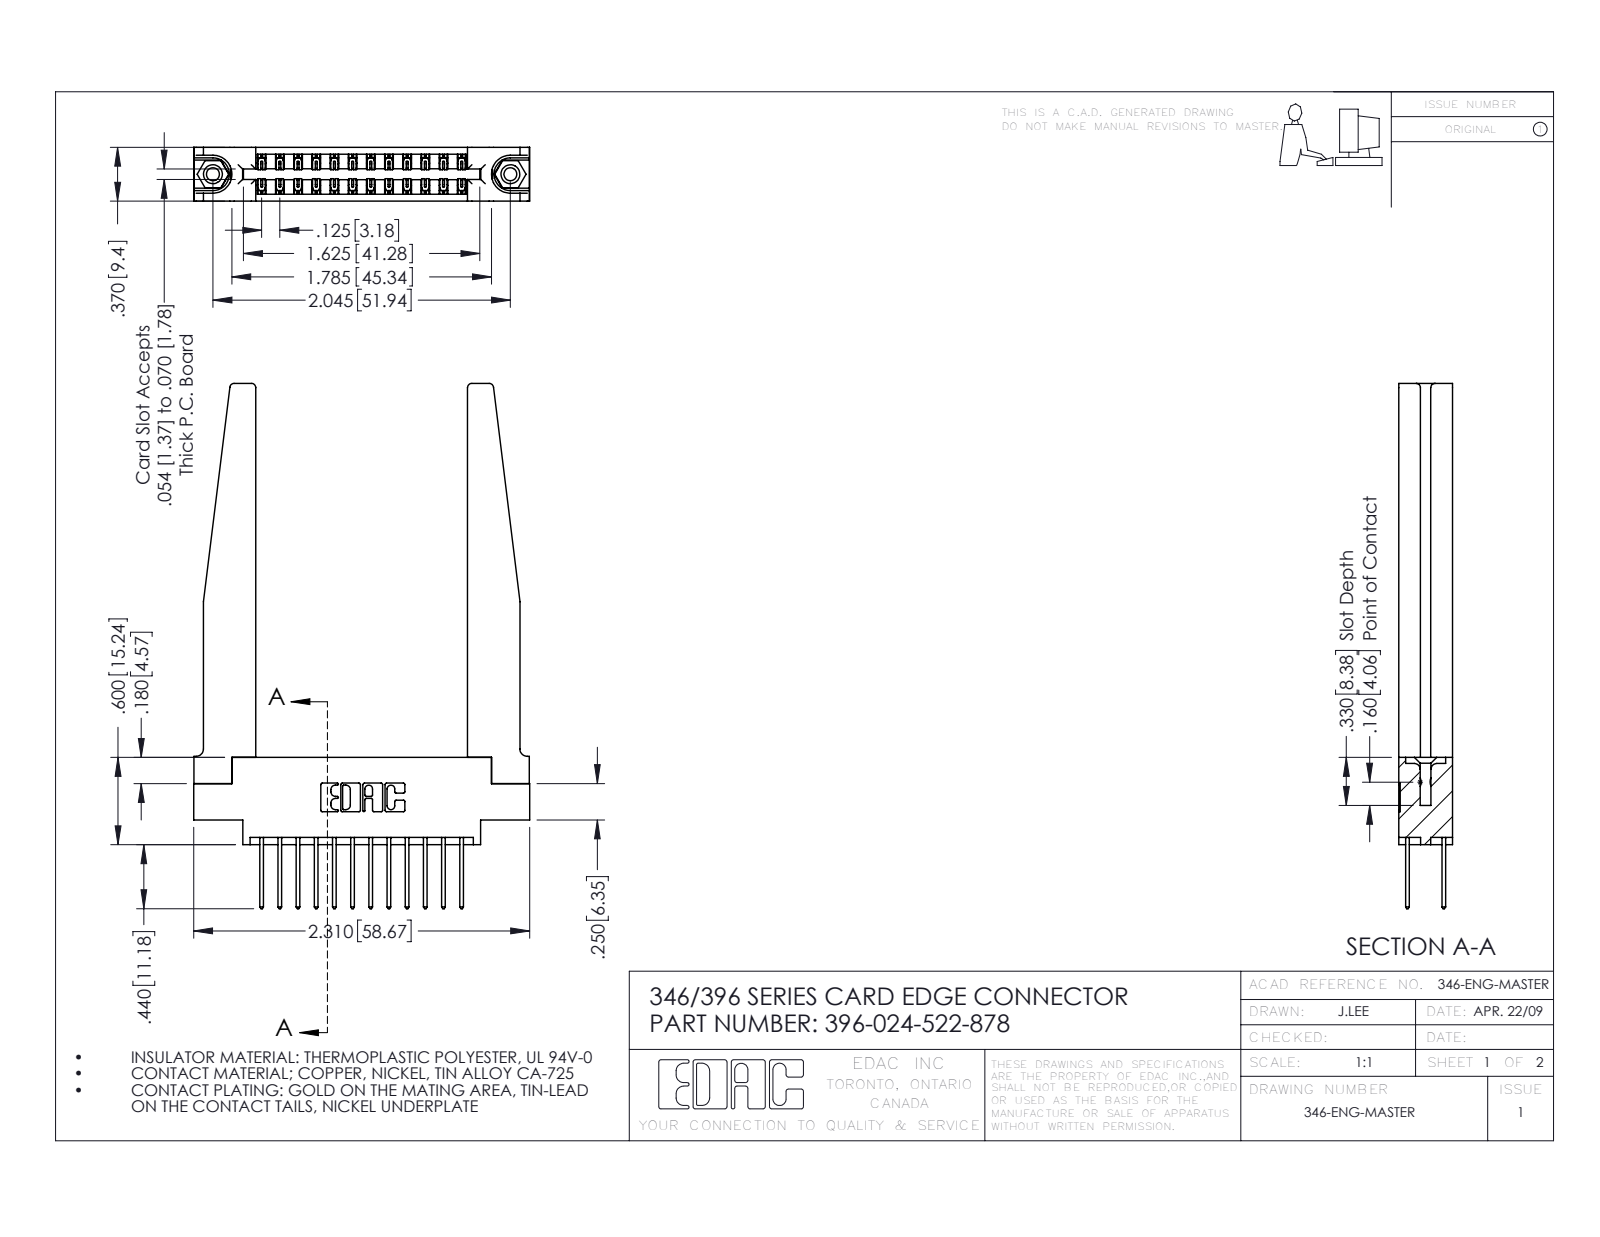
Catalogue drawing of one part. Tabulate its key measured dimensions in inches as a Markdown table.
| quantity | value |
| --- | --- |
| part name | 346 Part_0.170 Offset - 0.156 Dia-TH; 346-220-078_345-220-078; 396-024-522-878; 345-292-001_345-293-122 (+1 more) |
| STEP written by | SolidWorks 2016 (CONFIG_CONTROL_DESIGN) |
| units | inches |
| bodies | 29 solids, 1608 faces (1062 planar, 494 cylindrical, 52 other) |
| overall size | 3.61 × 2.31 × 0.37 |
| volume | 0.751 in³ |
| surface area | 21.62 in² |
| round holes (diameter × count) | 0.089 × 2, 0.125 × 2, 0.156 × 2, 0.064 × 1 |
| round bosses / shafts (diameter × count) | 0.155 × 2 |
| partial cylindrical surfaces (radius × count) | 0.006 × 36, 0.01 × 24, 0.01 × 22, 0.03 × 8, 0.007 × 6, 0.031 × 6, 0.026 × 3, 0.014 × 2 |
| main face-to-face distances | 0.37, 0.15, 0.072, 0.148, 0.048, 0.322, 0.25, 0.102, 0.22, 0.173 |
| hole center spacings | 0.246, 1.839, 2.045 |
